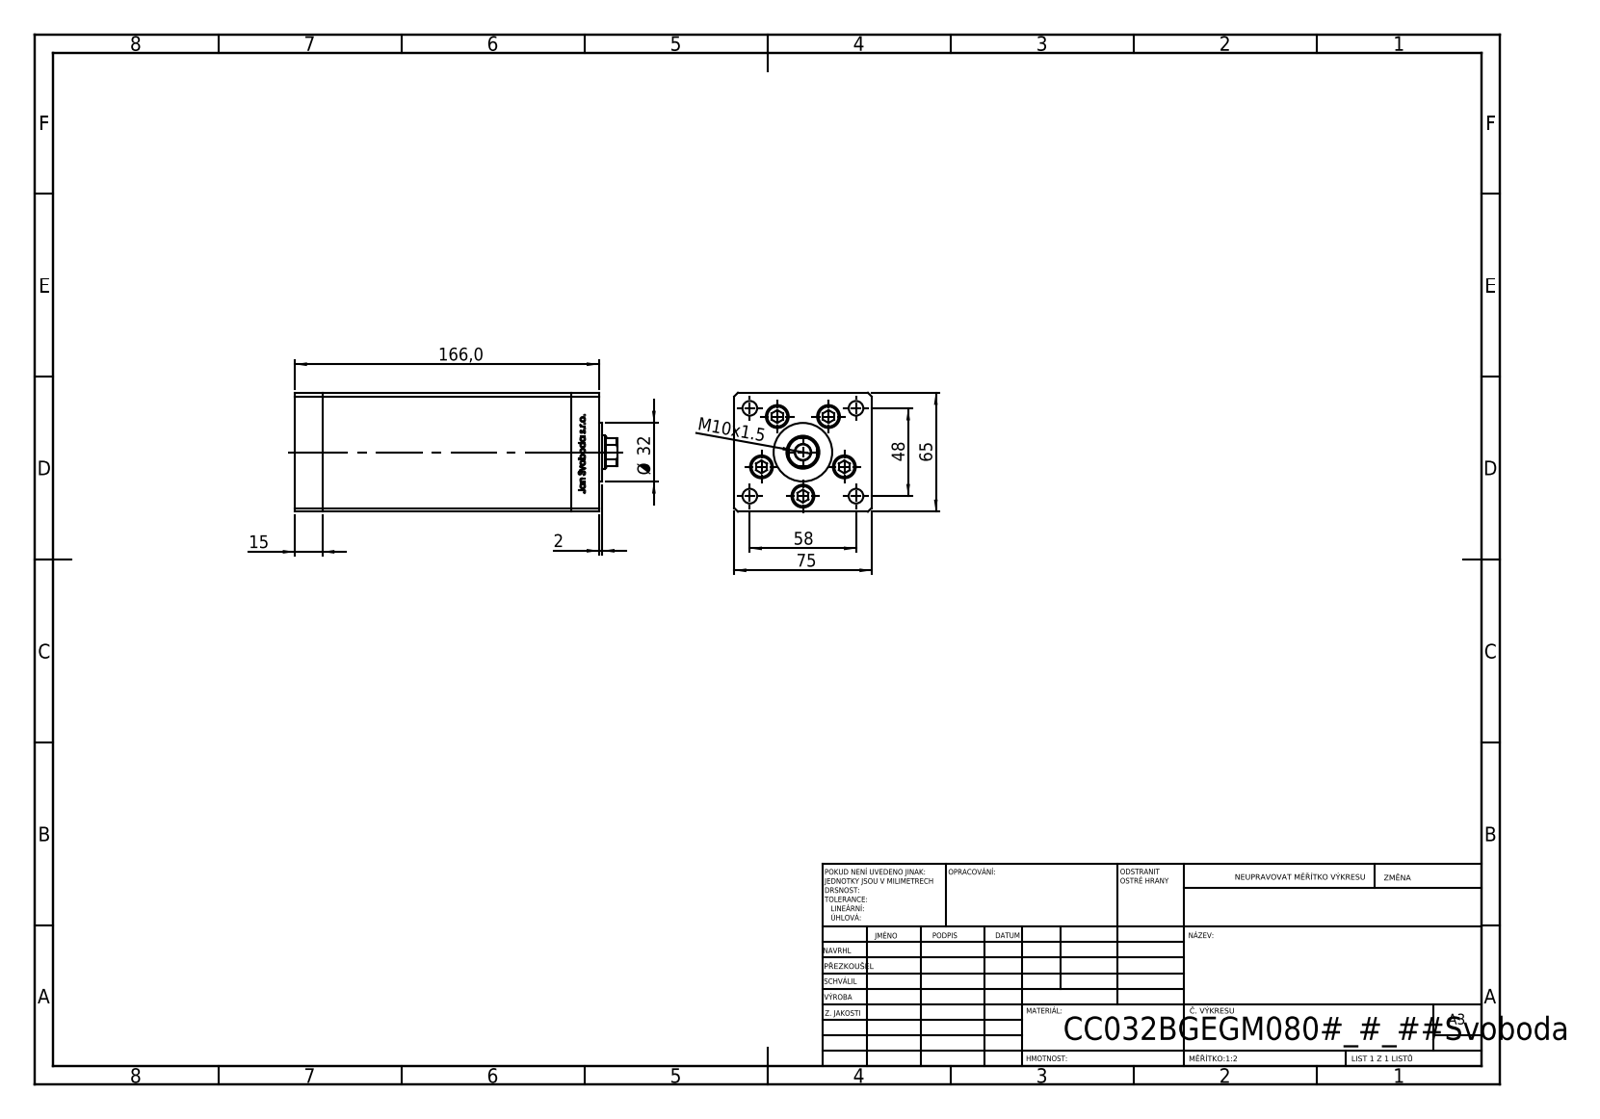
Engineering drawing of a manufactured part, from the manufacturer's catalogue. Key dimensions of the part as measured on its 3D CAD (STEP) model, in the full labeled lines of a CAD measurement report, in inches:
Part name (STEP PRODUCT): V220C_FRONT_B; ALLEN BOLT; V220C BACK_B; V220C_VC_B (+1 more)
STEP written by: SolidWorks 2019 (CONFIG_CONTROL_DESIGN)
Units: inches
Bodies: 14 solids, 1183 faces (462 planar, 147 cylindrical, 574 other)
Overall size (bounding box): 6.929 × 2.953 × 2.559
Volume: 44.09 in³ · Surface area: 197.4 in²
Round holes (diameter × count): ⌀0.354 ×5, ⌀0.492 ×5, ⌀0.315 ×4, ⌀0.079 ×2, ⌀0.518 ×2, ⌀0.335 ×1, ⌀0.709 ×1
Round bosses / shafts (diameter × count): ⌀0.315 ×5, ⌀1.26 ×1
Partial cylindrical surfaces — rounded edges, fillets, slot ends (radius × count): R0.037 ×2, R0.335 ×1
Main face-to-face distances: 2.953, 2.559, 0.591, 5.354, 5.945, 6.535, 1.102, 0.512, 2.146, 0.413
Hole centre spacings: 0.945, 1.482, 0.617, 0.678, 1.091, 1.135, 1.142, 1.285
